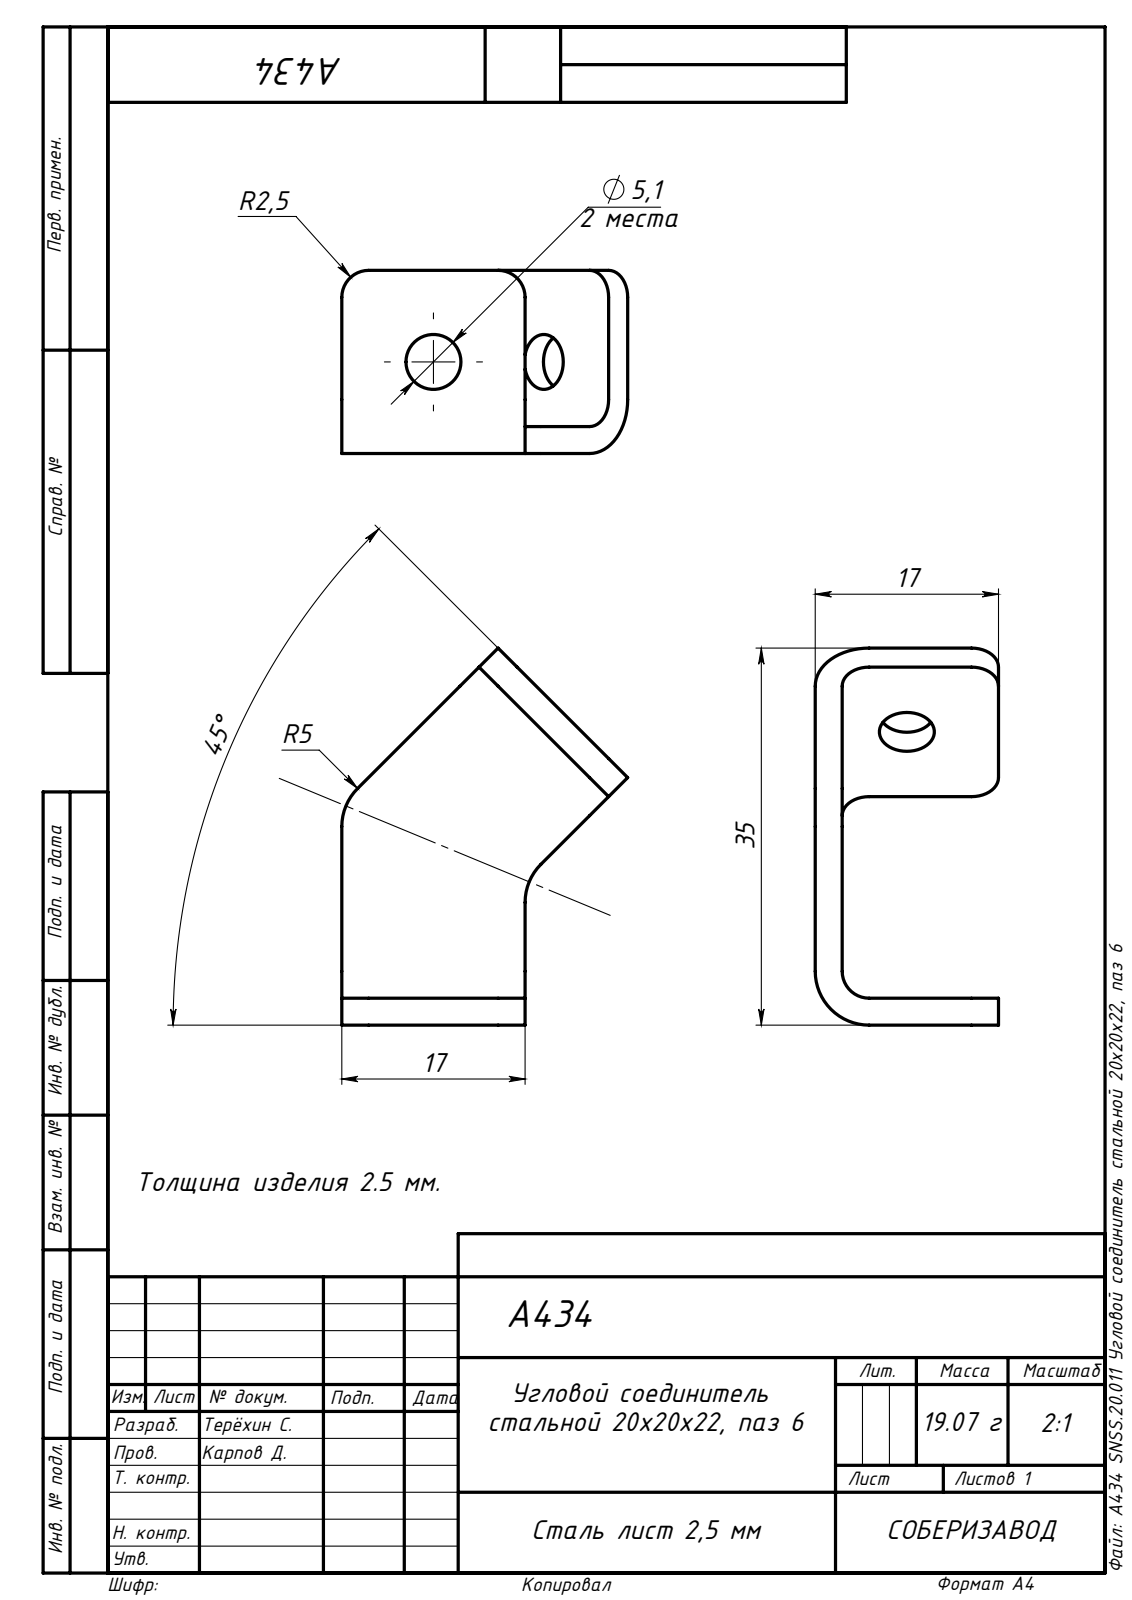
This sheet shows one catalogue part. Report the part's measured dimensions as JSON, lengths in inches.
{"part_name": "A434 SNSS.20.011 Угловой соединитель стальной 20х20х22, паз 6", "step_written_by": "SolidWorks 2020 (AUTOMOTIVE_DESIGN)", "units": "inches", "bodies": {"solids": 1, "faces": 34, "planar": 20, "cylindrical": 14, "other": 0}, "overall_size": [1.378, 1.044, 0.669], "volume_in3": 0.148, "surface_area_in2": 3.706, "round_holes": [[0.201, 2]], "partial_cylinders_radius": [[0.098, 6], [0.197, 4]], "face_to_face_distances": [0.098, 0.669, 0.571, 0.669]}
